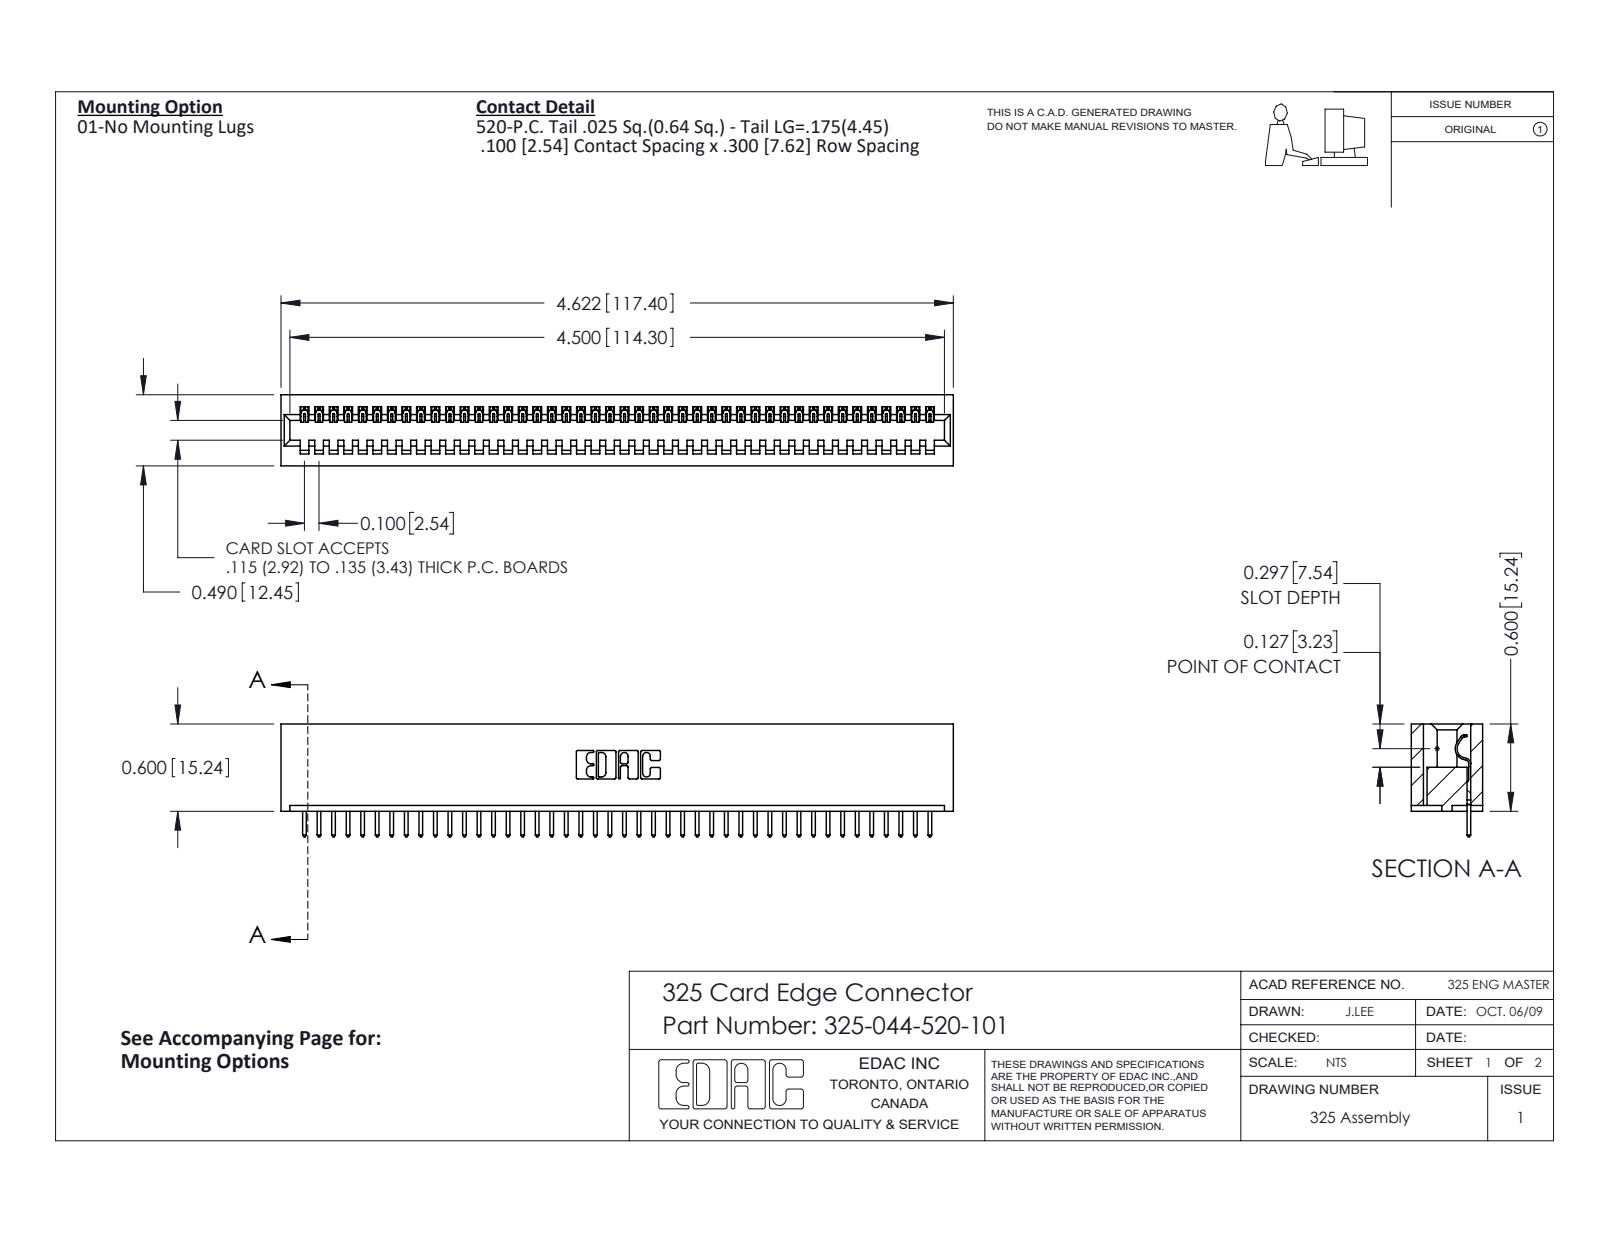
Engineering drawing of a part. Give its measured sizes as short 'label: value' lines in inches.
name: 325-044-520-101; 325-292-001_325-293-120; 325 Part_Lugless
written by: SolidWorks 2016 (CONFIG_CONTROL_DESIGN)
unit: in
bodies: 45 solids, 2658 faces (1914 planar, 744 cylindrical, 0 other)
size: 4.622 × 0.775 × 0.49
volume: 0.938 in³; area: 26.14 in²
rounds: 88× R0.006, 88× R0.01, 22× R0.01, 6× R0.007, 6× R0.031, 3× R0.026, 1× R0.014, 1× R0.022
face distances: 0.083, 0.407, 0.49, 0.3, 0.107, 0.383, 0.025, 0.325, 0.56, 0.263
